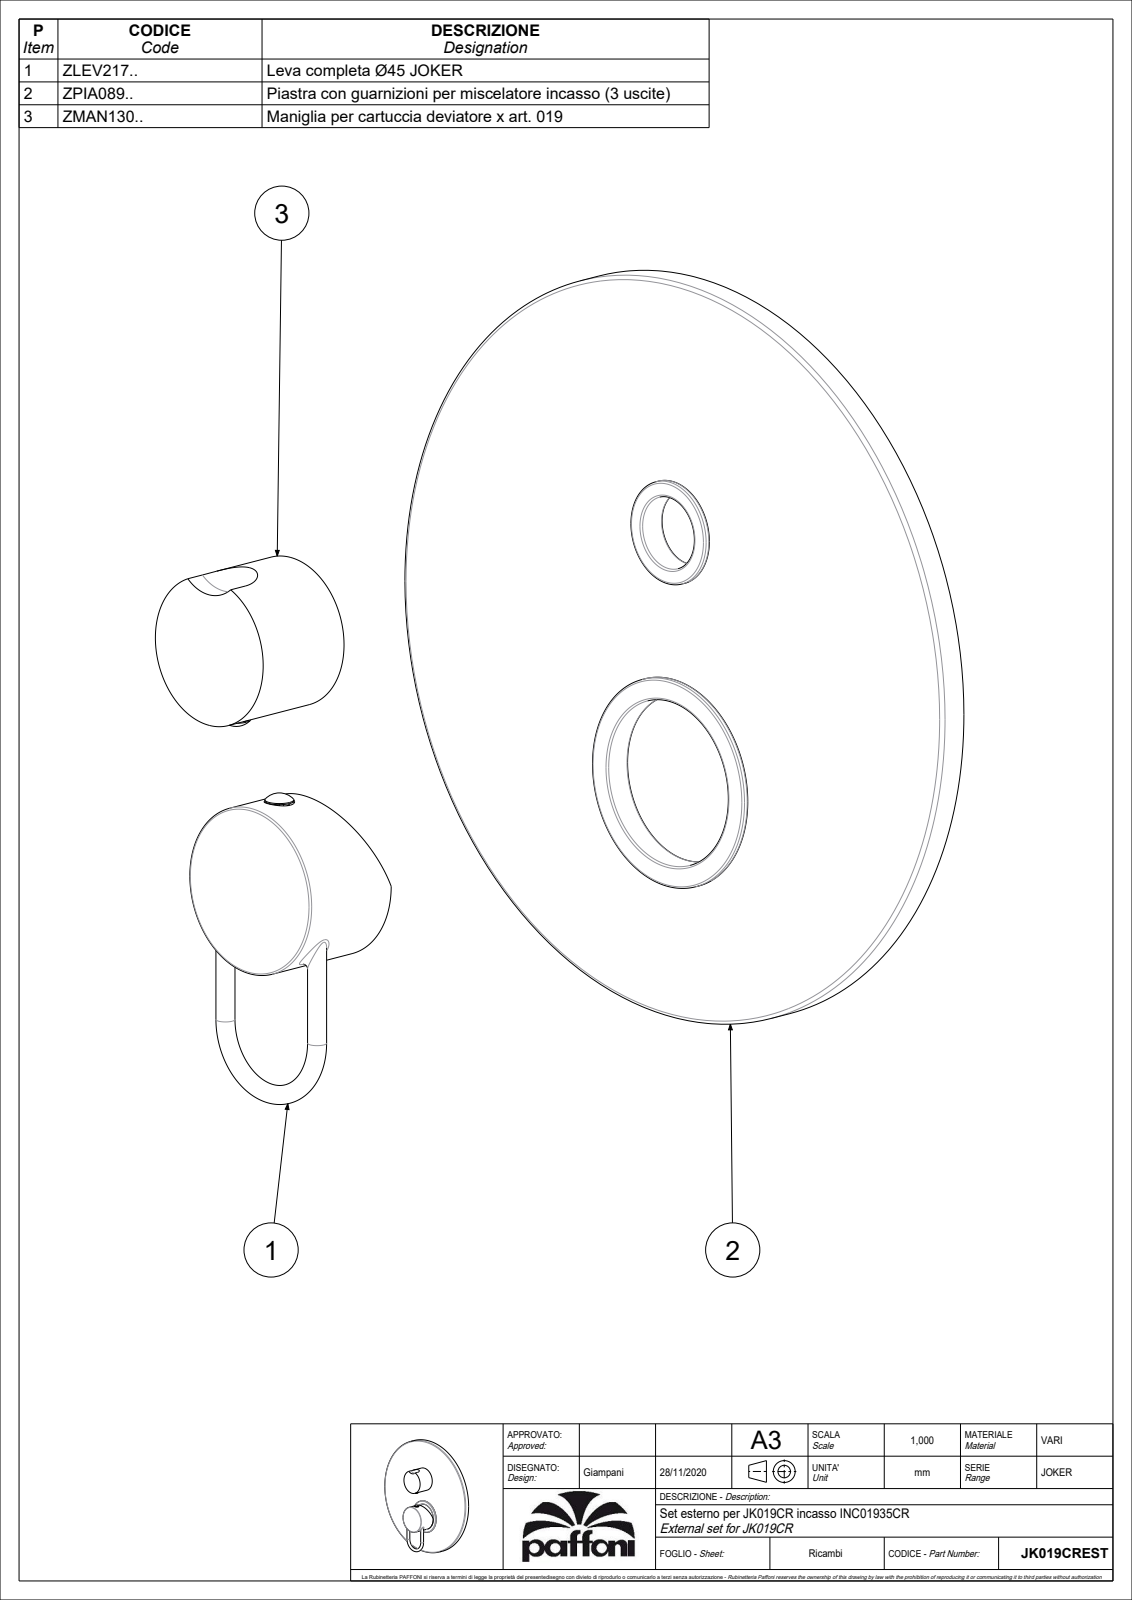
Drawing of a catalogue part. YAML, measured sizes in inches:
part_name: "JK018CREST"
step_written_by: "CREO PARAMETRIC BY PTC INC, 2020044 (CONFIG_CONTROL_DESIGN)"
units: inches
bodies: {solids: 3, faces: 239, planar: 80, cylindrical: 85, other: 74}
overall_size: [7.874, 7.874, 1.63]
volume: 11.24
surface_area: 158.9
round_holes:
  - {diameter: 0.118, count: 2}
  - {diameter: 0.126, count: 1}
  - {diameter: 0.165, count: 1}
  - {diameter: 0.315, count: 1}
  - {diameter: 0.583, count: 1}
  - {diameter: 0.752, count: 1}
  - {diameter: 1.417, count: 1}
  - {diameter: 1.756, count: 1}
  - {diameter: 1.969, count: 1}
  - {diameter: 5.709, count: 1}
  - {diameter: 7.795, count: 1}
round_bosses_or_shafts:
  - {diameter: 0.197, count: 4}
  - {diameter: 0.299, count: 2}
  - {diameter: 0.217, count: 2}
  - {diameter: 7.874, count: 1}
  - {diameter: 7.677, count: 1}
  - {diameter: 2.213, count: 1}
  - {diameter: 1.965, count: 1}
  - {diameter: 1.772, count: 1}
partial_cylinders:
  - {radius: 0.061, count: 2}
  - {radius: 0.492, count: 1}
face_to_face_distances: [0.039, 0.315, 0.354, 0.433, 1.102, 0.079, 0.118, 1.142, 1.024, 1.457]
hole_center_spacings: [0.039, 0.394, 1.268, 1.409, 1.661, 2.677, 3.071]
